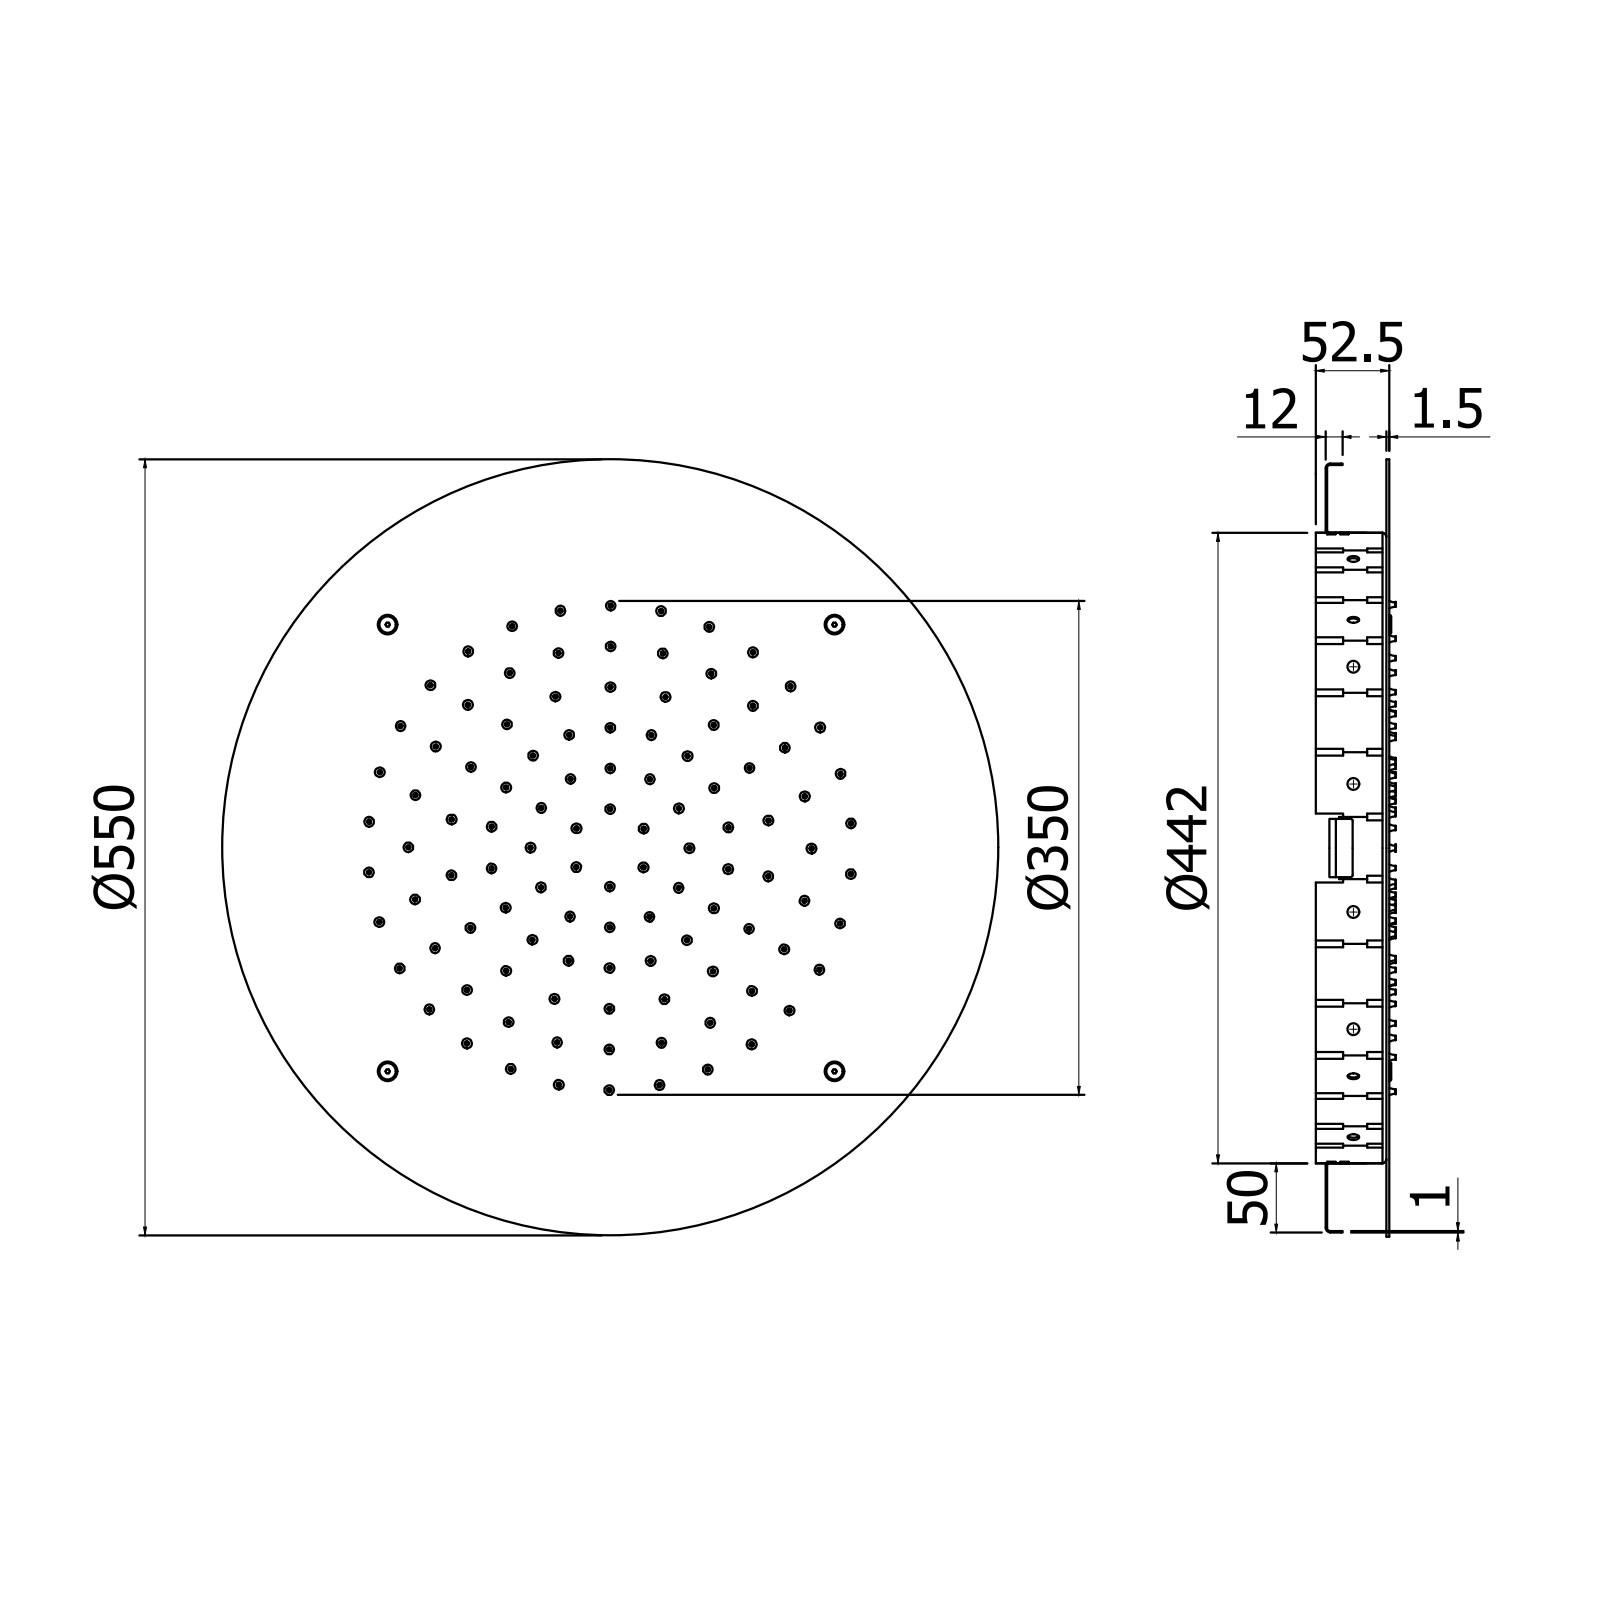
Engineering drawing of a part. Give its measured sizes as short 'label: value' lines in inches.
name: ZSOF304CR
written by: CREO PARAMETRIC BY PTC INC, 2020044 (CONFIG_CONTROL_DESIGN)
unit: in
bodies: 1 solid, 1962 faces (156 planar, 538 cylindrical, 1268 other)
size: 21.654 × 21.654 × 0.189
volume: 21.79 in³; area: 755.9 in²
holes: 126× ⌀0.059, 126× ⌀0.197
bosses: 4× ⌀0.394, 1× ⌀21.654
rounds: 24× R0.008
face distances: 0.059, 0.039, 0.098, 0.091, 0.13, 0.189, 0.079, 12.594, 0.079, 15.793
hole spacings: 3.107, 4.925, 6.533, 9.59, 9.985, 10.085, 2.393, 2.563
